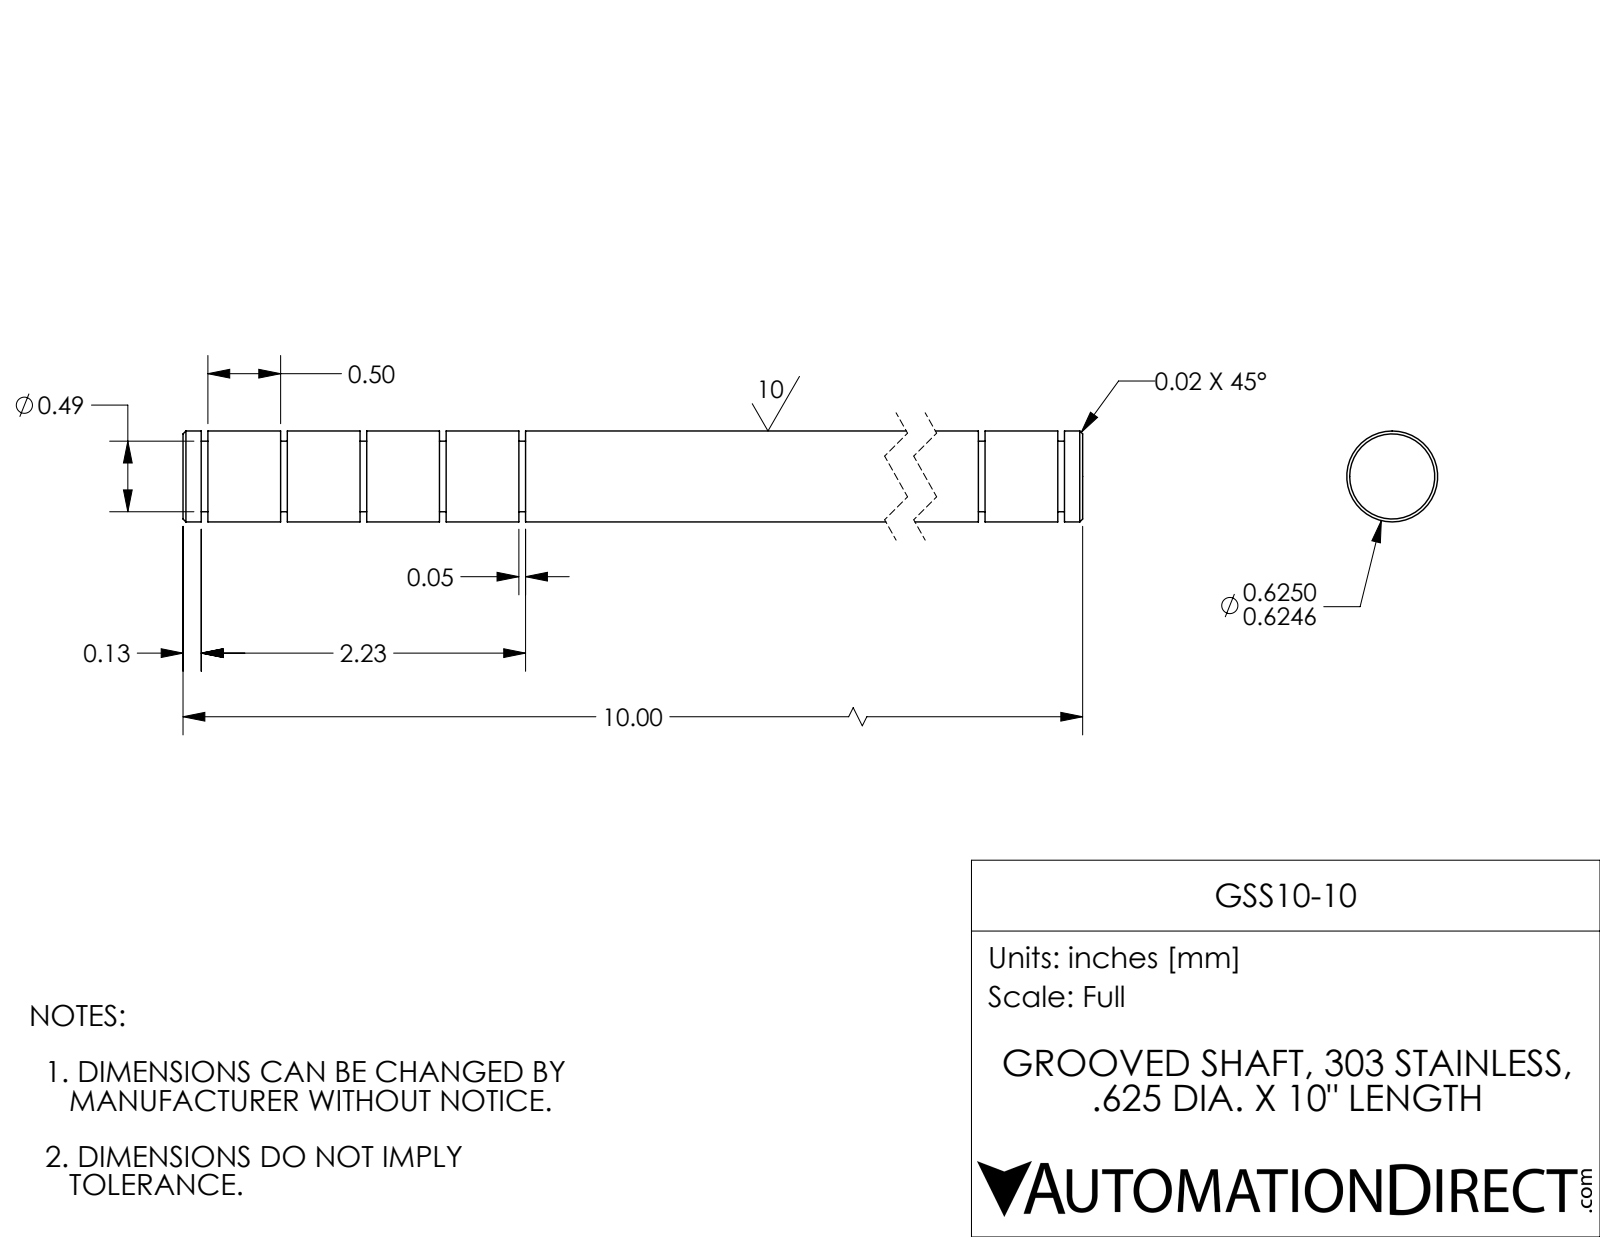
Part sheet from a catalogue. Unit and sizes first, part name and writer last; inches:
Units: inches
Overall size (bounding box): 10 × 0.625 × 0.625
Round bosses / shafts (diameter × count): ⌀0.625 ×1, ⌀0.485 ×1
Main face-to-face distances: 0.546, 0.046, 1.092, 0.5, 0.592, 1.638, 1.138, 9.158, 1.046, 8.612
Volume: 3.028 in³ · Surface area: 21.77 in²
Bodies: 1 solid, 50 faces (16 planar, 30 cylindrical, 4 other)
Part name (STEP PRODUCT): GSS10-10
STEP written by: SolidWorks 2017 (AUTOMOTIVE_DESIGN)
